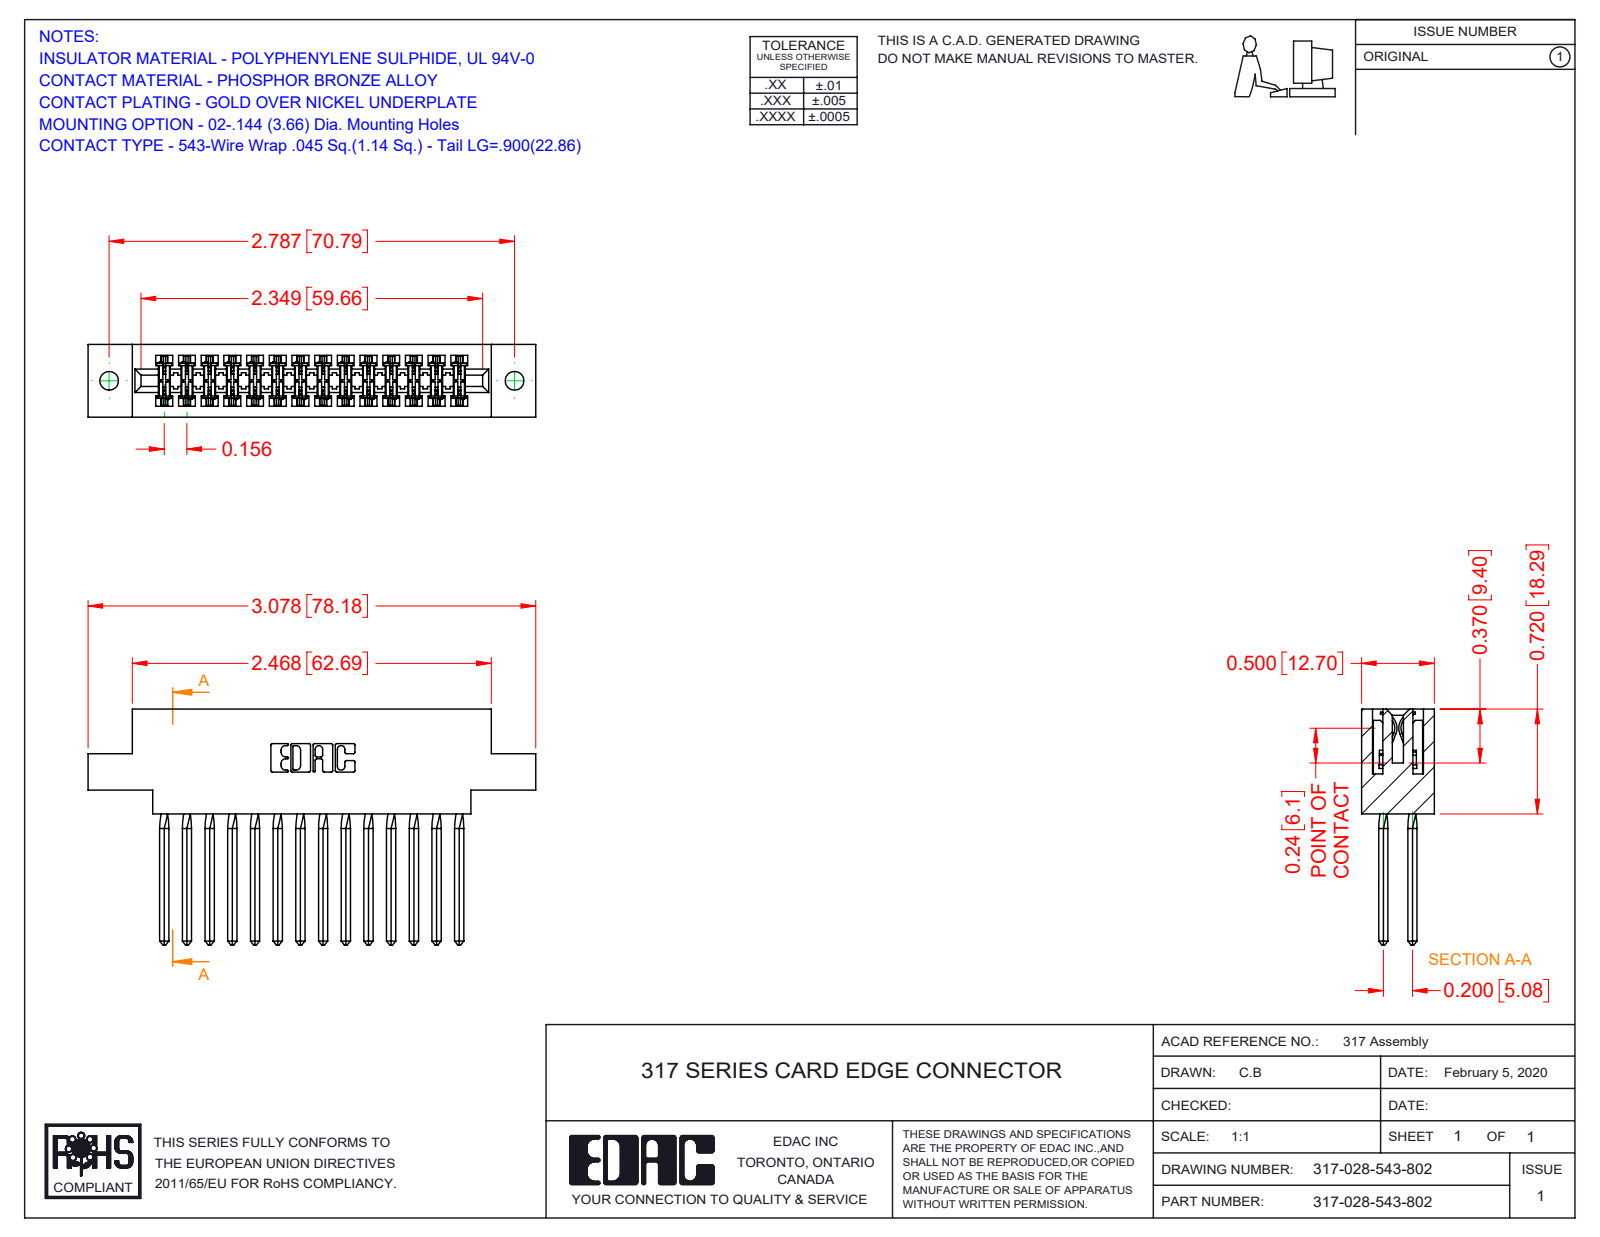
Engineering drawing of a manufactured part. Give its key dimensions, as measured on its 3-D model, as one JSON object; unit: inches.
{"part_name": "317-290-001_543; 317-028-543-802; 317 Part_.144 Dia", "step_written_by": "SolidWorks 2016 (CONFIG_CONTROL_DESIGN)", "units": "inches", "bodies": {"solids": 29, "faces": 2594, "planar": 2102, "cylindrical": 380, "other": 112}, "overall_size": [3.078, 1.62, 0.5], "volume_in3": 0.749, "surface_area_in2": 26.76, "round_holes": [[0.128, 2]], "partial_cylinders_radius": [[0.015, 56], [0.01, 22], [0.007, 6], [0.031, 6], [0.026, 3], [0.095, 2], [0.1, 2], [0.11, 2]], "face_to_face_distances": [0.5, 0.075, 0.425, 0.11, 0.22, 0.35, 0.331, 0.116, 0.72, 0.195], "hole_center_spacings": [2.787]}
